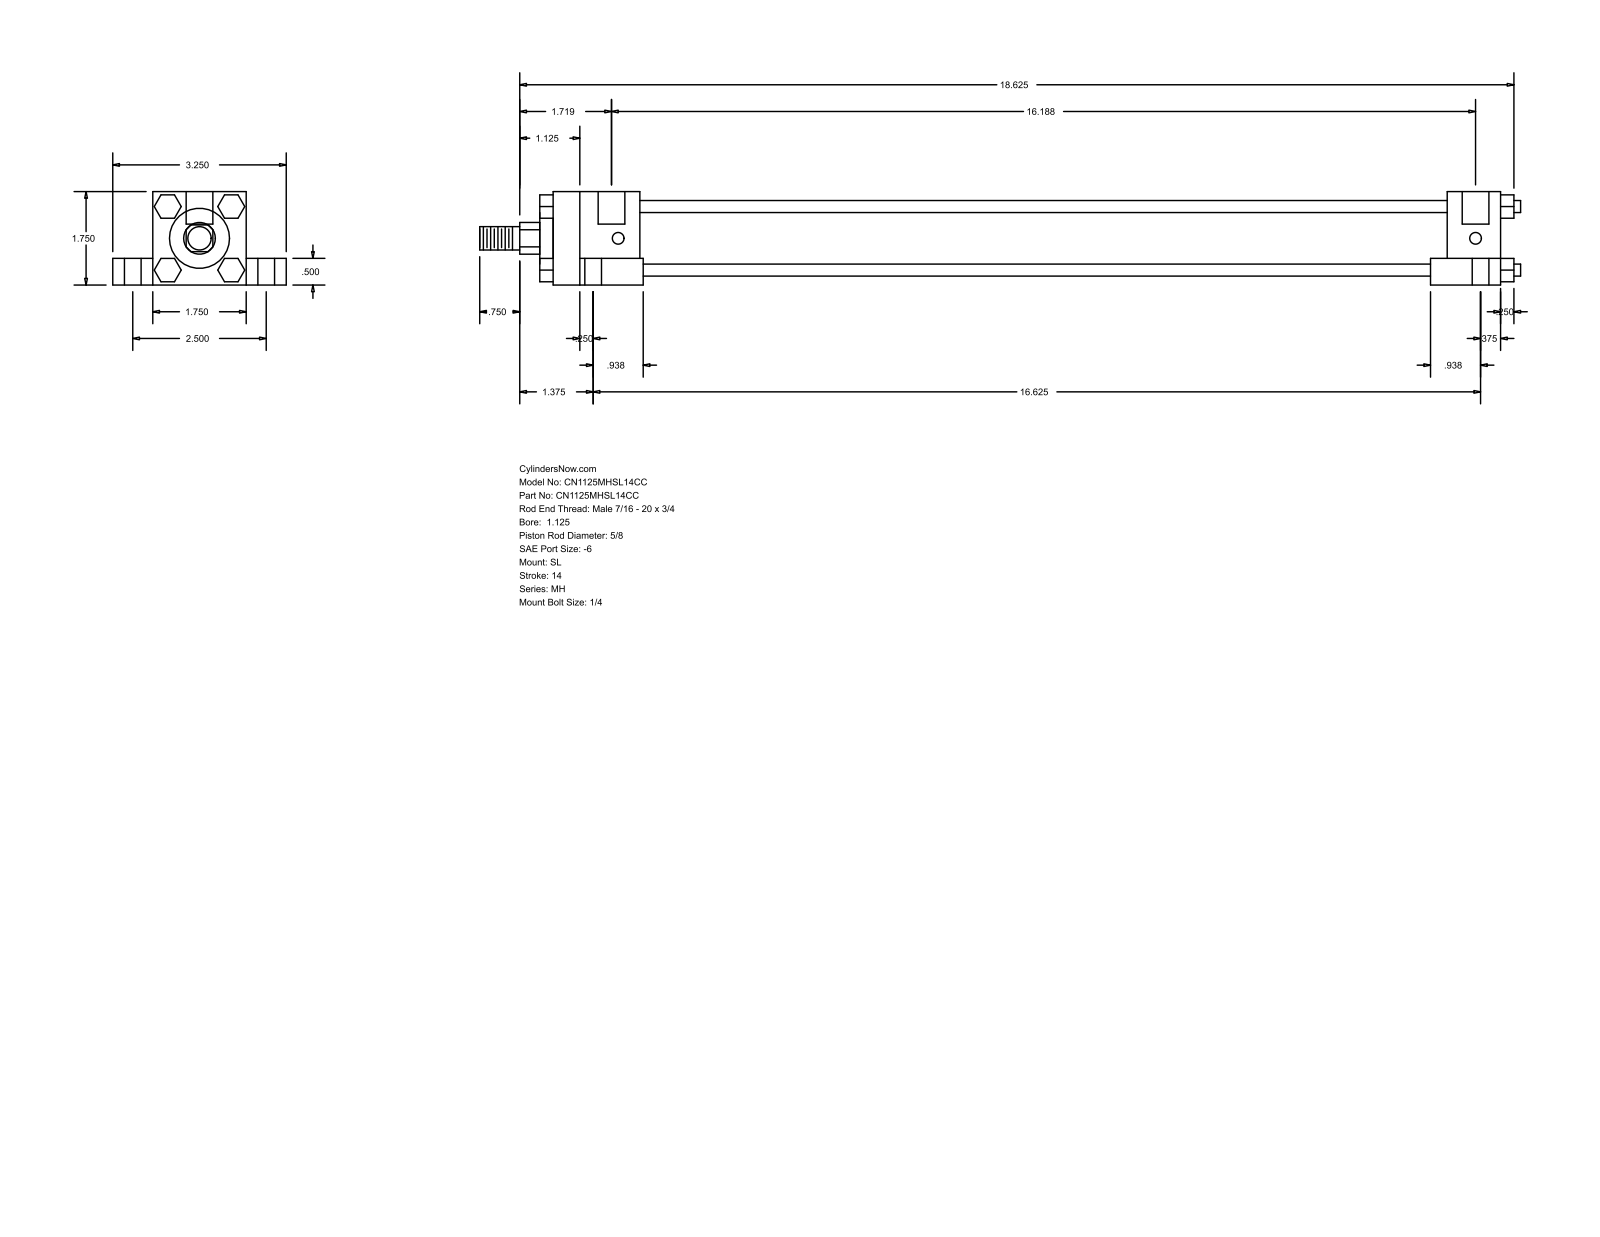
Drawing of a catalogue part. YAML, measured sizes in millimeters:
part_name: "MH_SL__0112_0.625"
step_written_by: "GSSL Pune (CONFIG_CONTROL_DESIGN)"
units: millimeters
bodies: {solids: 0, faces: 150, planar: 114, cylindrical: 36, other: 0}
overall_size: [495.3, 82.55, 44.45]
round_holes:
  - {diameter: 5.56, count: 4}
  - {diameter: 7.94, count: 4}
  - {diameter: 14.29, count: 4}
  - {diameter: 12.7, count: 2}
round_bosses_or_shafts:
  - {diameter: 5.71, count: 4}
  - {diameter: 34.92, count: 1}
  - {diameter: 28.57, count: 1}
  - {diameter: 15.88, count: 1}
  - {diameter: 11.11, count: 1}
partial_cylinders:
  - {radius: 7.54, count: 1}
face_to_face_distances: [44.46, 19.04, 12.7, 31.76, 63.5, 11.11, 47.62, 33.34, 404.82, 384.17]
hole_center_spacings: [31.84, 32.23, 32.93, 63.5, 407.99, 411.6, 414.76, 417.93]
